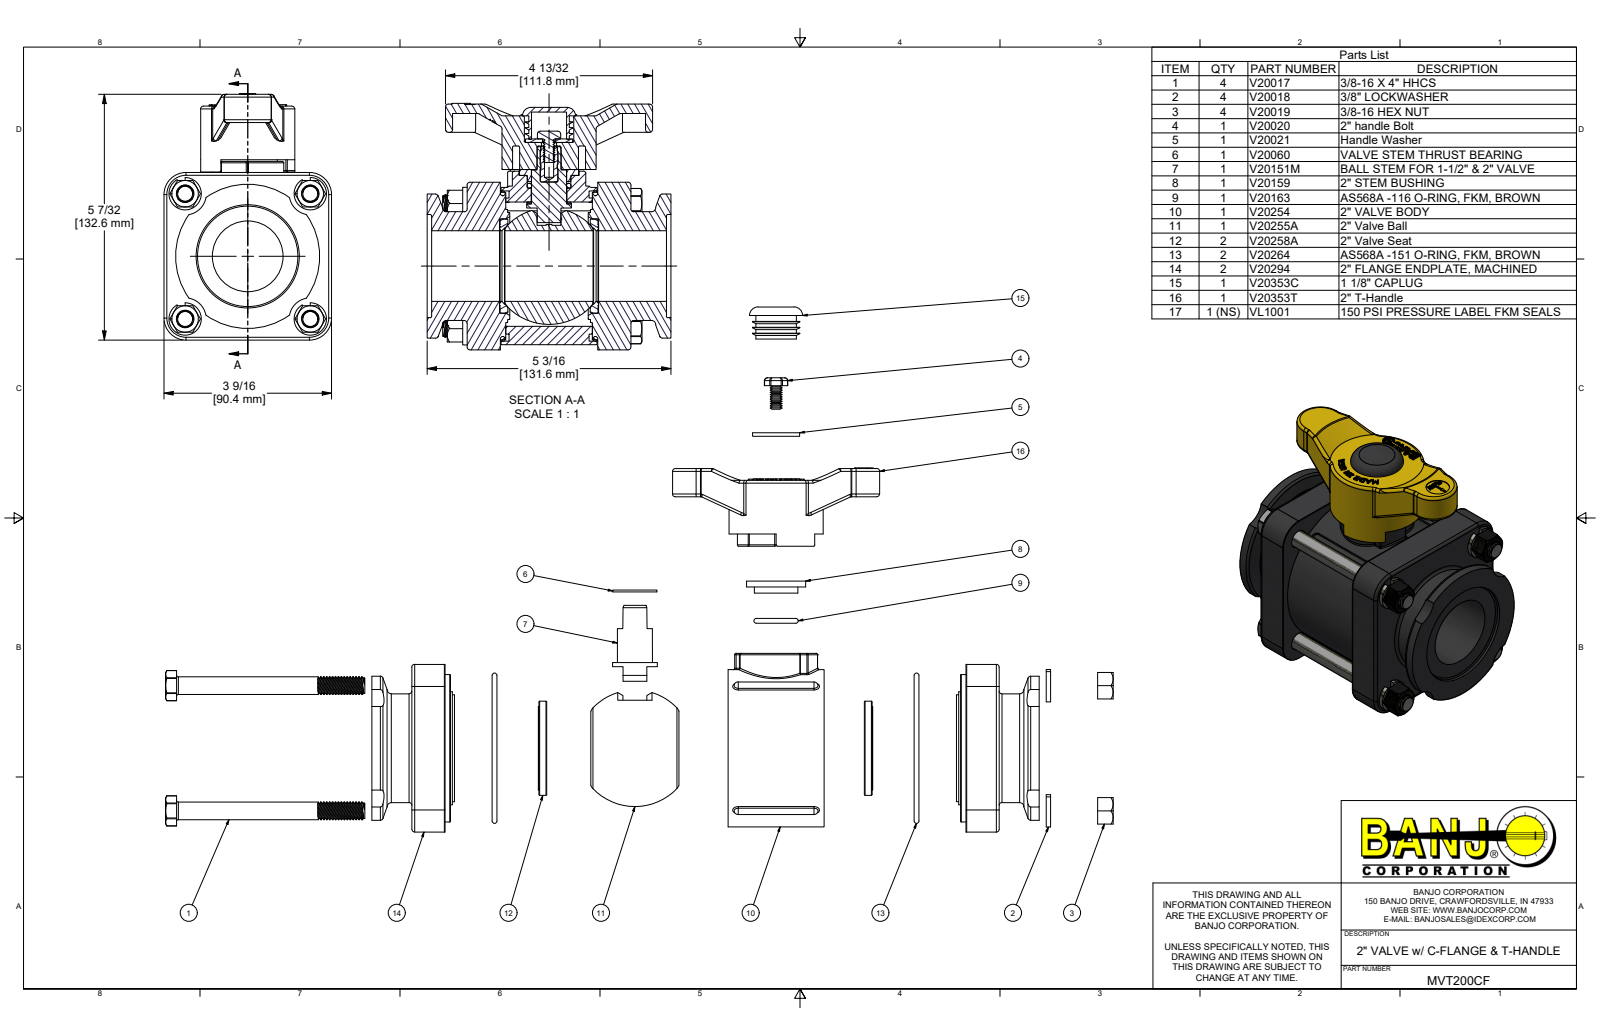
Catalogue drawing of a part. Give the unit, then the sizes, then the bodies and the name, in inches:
Units: inches
Overall size (bounding box): 5.235 × 5.18 × 3.56
Round holes (diameter × count): ⌀0.165 ×10, ⌀0.307 ×4, ⌀0.385 ×4, ⌀0.406 ×4, ⌀0.172 ×1, ⌀0.196 ×1, ⌀0.244 ×1, ⌀0.281 ×1, ⌀0.32 ×1, ⌀0.351 ×1, ⌀0.375 ×1, ⌀0.5 ×1
Round bosses / shafts (diameter × count): ⌀0.324 ×60, ⌀0.687 ×4, ⌀0.375 ×4, ⌀2 ×2, ⌀3.13 ×1, ⌀2.89 ×1, ⌀2.4 ×1, ⌀2.31 ×1
Partial cylindrical surfaces — rounded edges, fillets, slot ends (radius × count): R0.06 ×54, R0.03 ×42, R0.075 ×8, R0.162 ×8, R0.125 ×5, R0.015 ×4, R0.094 ×4, R0.32 ×4
Main face-to-face distances: 0.82, 0.705, 2.775, 2.66, 0.115, 1.955, 1.67, 0.85, 3.48, 1.555
Hole centre spacings: 1.363, 2.322, 2.632, 0.705, 0.977, 1.682, 2.36, 2.82
Volume: 39.37 in³ · Surface area: 291.3 in²
Bodies: 30 solids, 1882 faces (676 planar, 545 cylindrical, 661 other)
Part name (STEP PRODUCT): MVT200CF; V20254; VL1001-D3.340; V20151M (+8 more)
STEP written by: Autodesk Inventor 2022 (AUTOMOTIVE_DESIGN)
